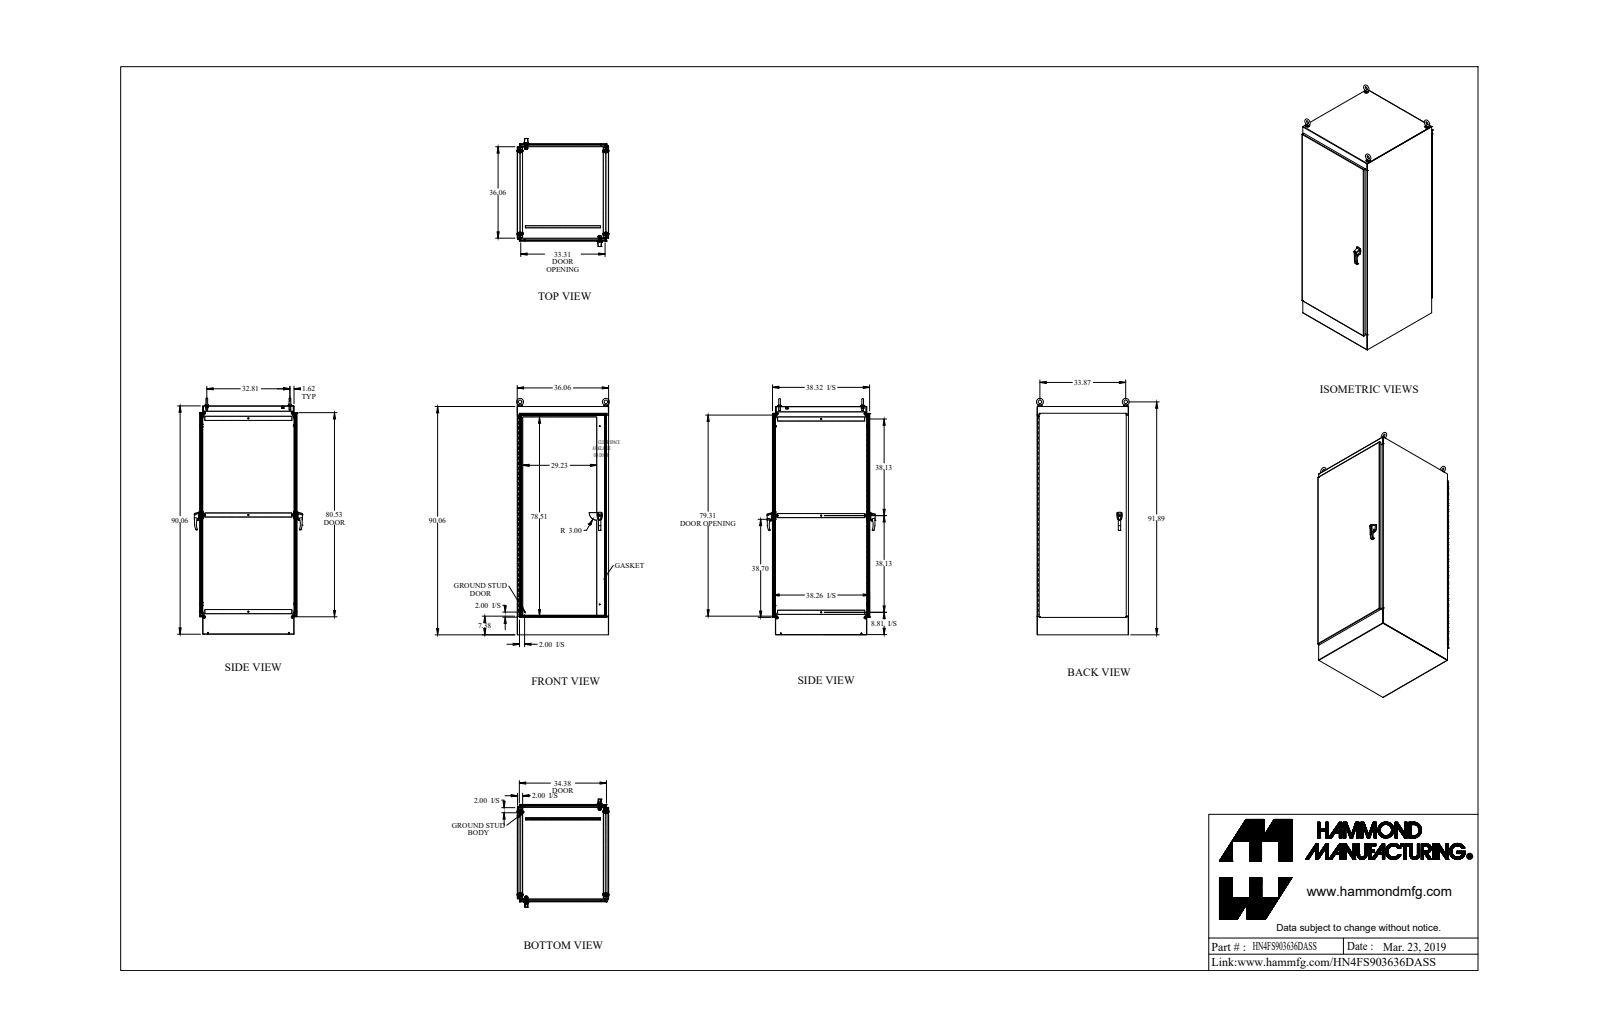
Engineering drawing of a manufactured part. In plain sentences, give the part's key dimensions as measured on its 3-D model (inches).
The part is named "HN4FS903636DASS". Its 3-D file was written by "SolidWorks 2018 (AUTOMOTIVE_DESIGN)". It is 91 solids with 3633 faces: 1578 planar, 1727 cylindrical and 328 other. Overall it measures 93.489 by 42.664 by 36.604 inches. Its volume is 1 842 cubic inches and its surface area 38 839 square inches. Round holes: 26 of diameter 0.304, 8 of diameter 0.35, 4 of diameter 0.25, 4 of diameter 0.257, 4 of diameter 0.28, 4 of diameter 0.281, 4 of diameter 0.313, 4 of diameter 0.39, 4 of diameter 0.413, 4 of diameter 0.625, 4 of diameter 0.68, 4 of diameter 0.75. Round bosses or shafts: 4 of diameter 1.75, 4 of diameter 1.5, 4 of diameter 1.25, 4 of diameter 1, 4 of diameter 0.75, 4 of diameter 0.738, 4 of diameter 0.63, 4 of diameter 0.625. Partial cylindrical surfaces (rounded edges, fillets, slot ends): 44 of radius 0.125, 42 of radius 0.043, 36 of radius 0.138, 32 of radius 0.018, 26 of radius 0.048, 26 of radius 0.143, 26 of radius 0.5, 21 of radius 0.06. The main face-to-face distances are 0.095, 35.965, 38.339, 35.87, 36.06, 38.244, 38.434, 89.965, 1.187, 37.152. The hole center spacings are 6, 12, 34.849, 18, 36.365, 38.761, 24, 41.886.
